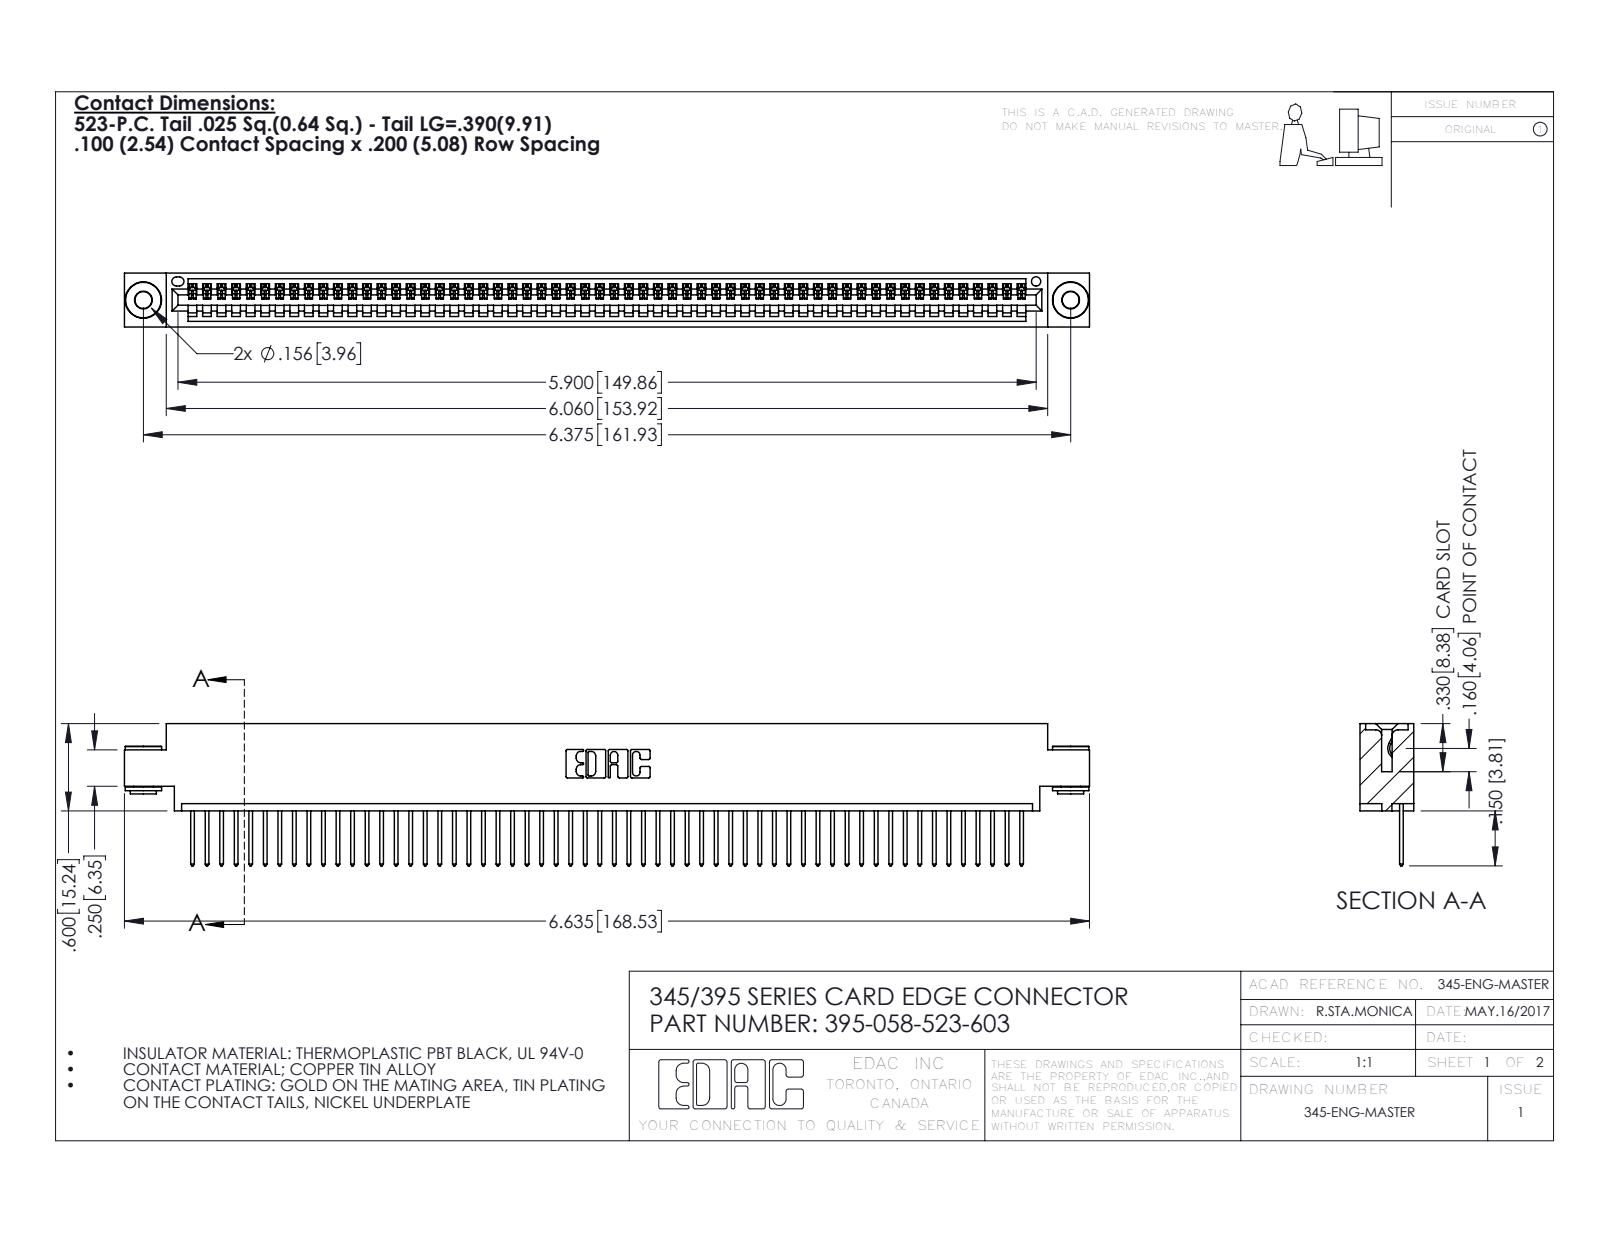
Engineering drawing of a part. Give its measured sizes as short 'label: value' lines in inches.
name: 345-292-001_345-293-123; 345-250-002_345-250-002-102; 395-058-523-603; 345 Part_0.170 Offset - 0.156 Dia-TH
written by: SolidWorks 2016 (CONFIG_CONTROL_DESIGN)
unit: in
bodies: 61 solids, 3532 faces (2414 planar, 1110 cylindrical, 8 other)
size: 6.635 × 0.977 × 0.37
volume: 0.978 in³; area: 33.97 in²
holes: 2× ⌀0.116, 2× ⌀0.156, 1× ⌀0.064
bosses: 2× ⌀0.25, 2× ⌀0.18, 2× ⌀0.136
rounds: 116× R0.006, 116× R0.01, 22× R0.01, 6× R0.007, 6× R0.031, 3× R0.026, 2× R0.031, 2× R0.04
face distances: 0.072, 0.298, 0.37, 0.098, 0.272, 0.025, 0.2, 0.225, 0.175, 0.149
hole spacings: 0.27, 6.139, 6.375
